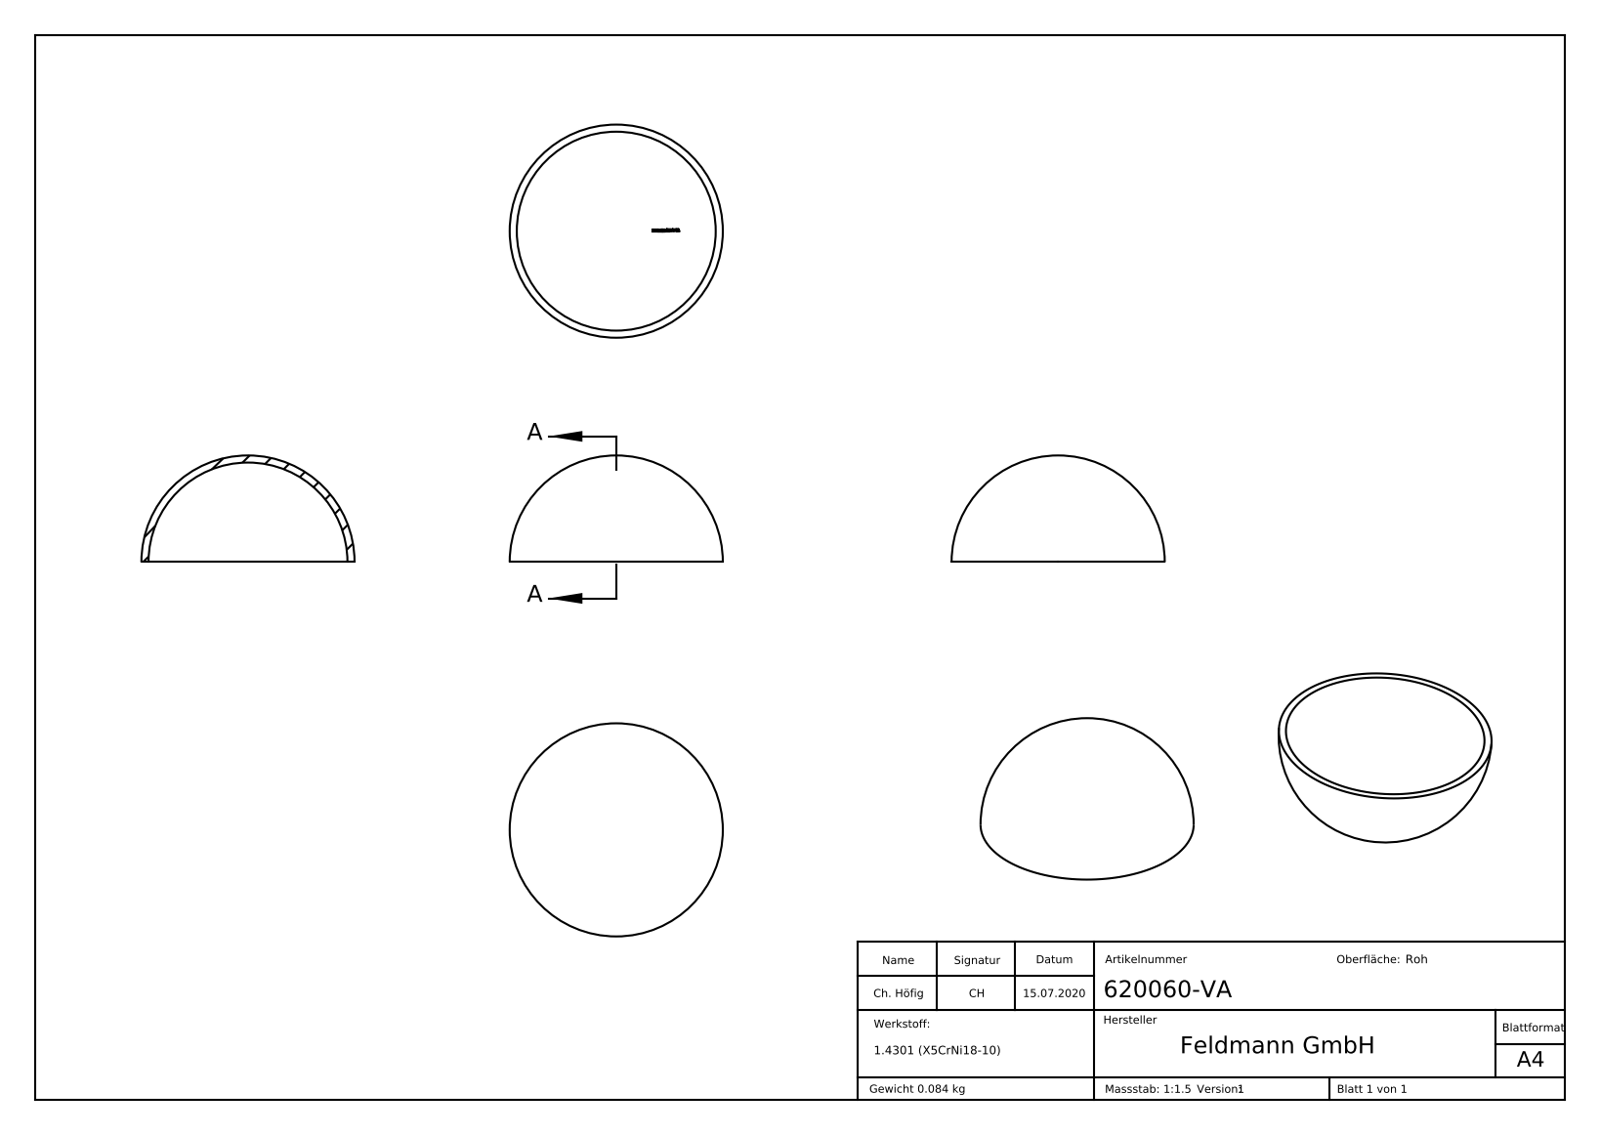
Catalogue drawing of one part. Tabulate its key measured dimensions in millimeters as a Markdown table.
| quantity | value |
| --- | --- |
| part name | 620060-VA |
| STEP written by | SolidWorks 2018 (CONFIG_CONTROL_DESIGN) |
| units | millimeters |
| bodies | 1 solid, 216 faces (89 planar, 0 cylindrical, 127 other) |
| overall size | 60 × 60 × 30 |
| volume | 10 572 mm³ |
| surface area | 10 950 mm² |
| main face-to-face distances | 0.45, 0.5, 1.36, 0.61, 1.19, 0.53, 0.55, 0.31, 0.81, 1.31 |
